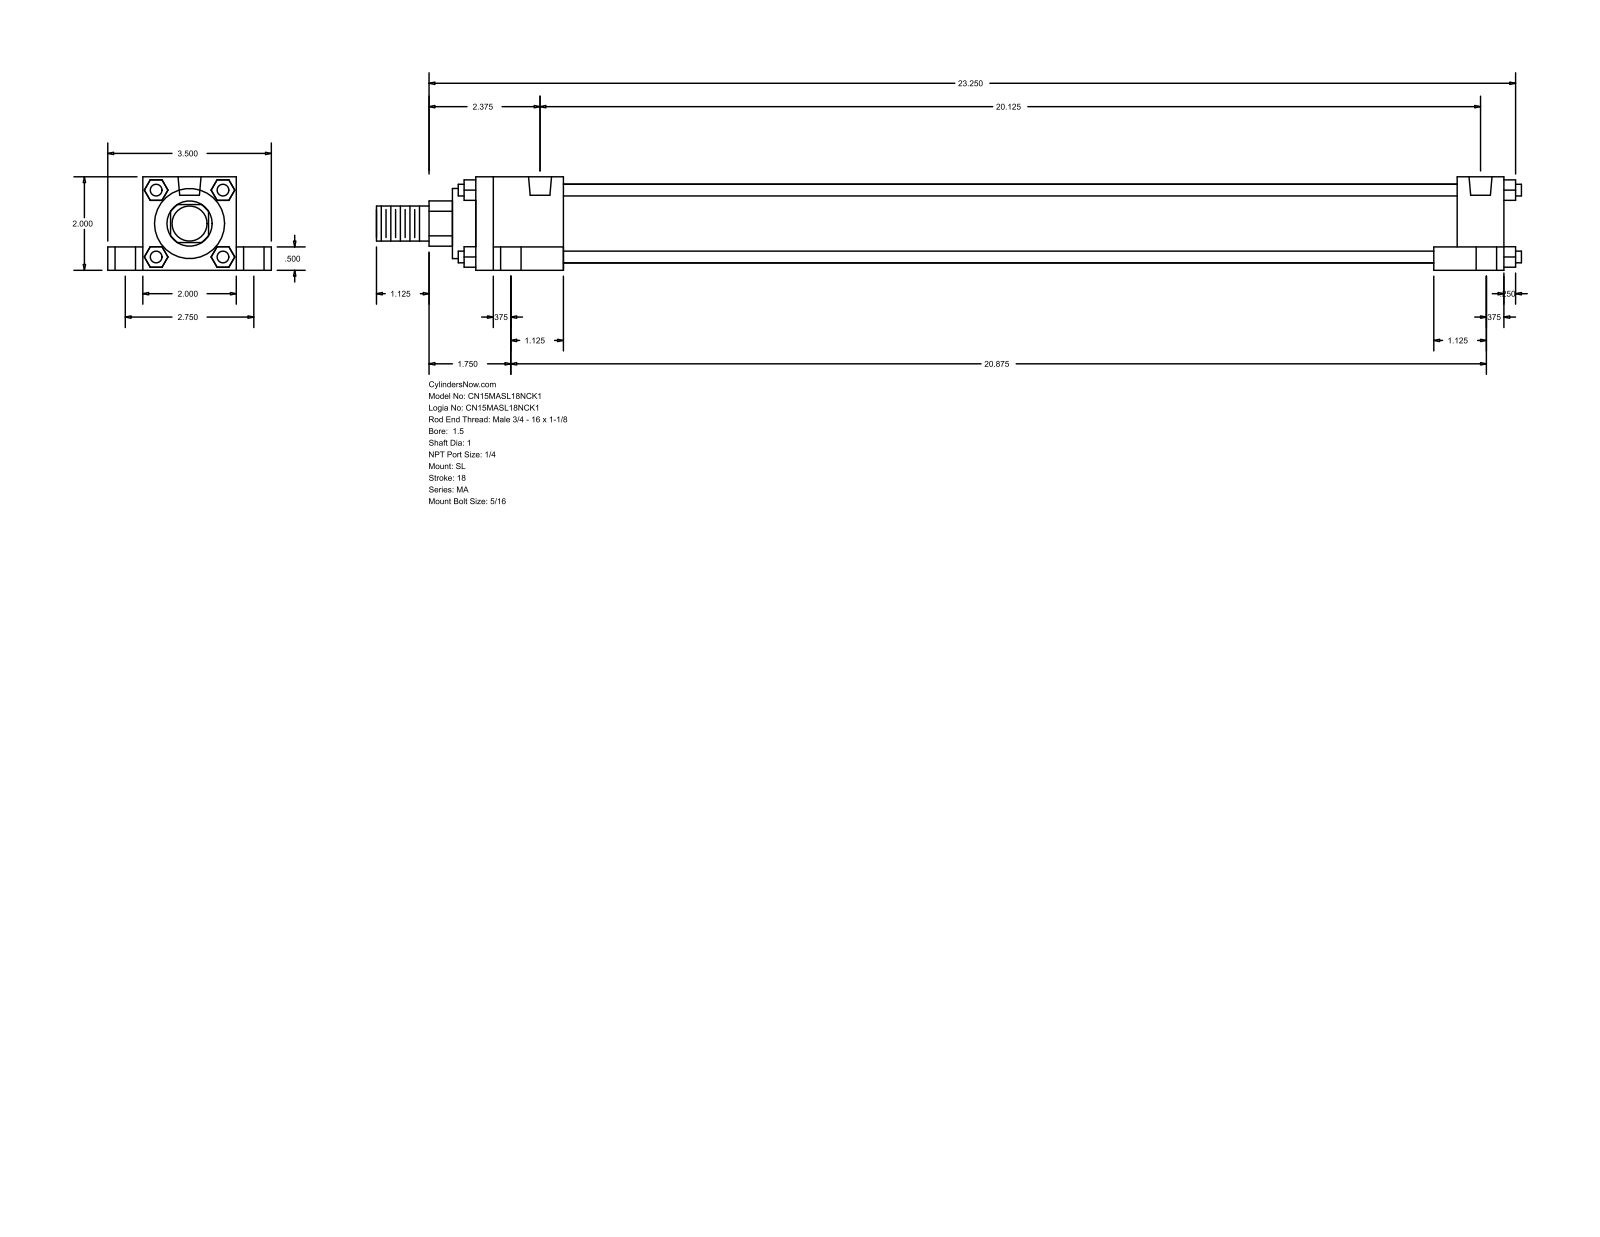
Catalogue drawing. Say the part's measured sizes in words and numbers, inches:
The part is named "MA_SL__0150_1". Its 3-D file was written by "GSSL Pune (CONFIG_CONTROL_DESIGN)". It is 0 solids with 148 faces: 112 planar, 36 cylindrical and 0 other. Overall it measures 24.5 by 3.5 by 2 inches. Round holes: 4 of diameter 0.313, 4 of diameter 0.437, 4 of diameter 0.687, 2 of diameter 0.492. Round bosses or shafts: 4 of diameter 0.25, 1 of diameter 1.69, 1 of diameter 1.5, 1 of diameter 1, 1 of diameter 0.75. Partial cylindrical surfaces (rounded edges, fillets, slot ends): 1 of radius 0.484. The main face-to-face distances are 2, 0.5, 0.75, 2.75, 1.5, 0.375, 22, 1, 0.25, 21. The hole center spacings are 1.38, 1.51, 2.75, 20.125, 20.296, 20.796, 20.875, 21.055.
